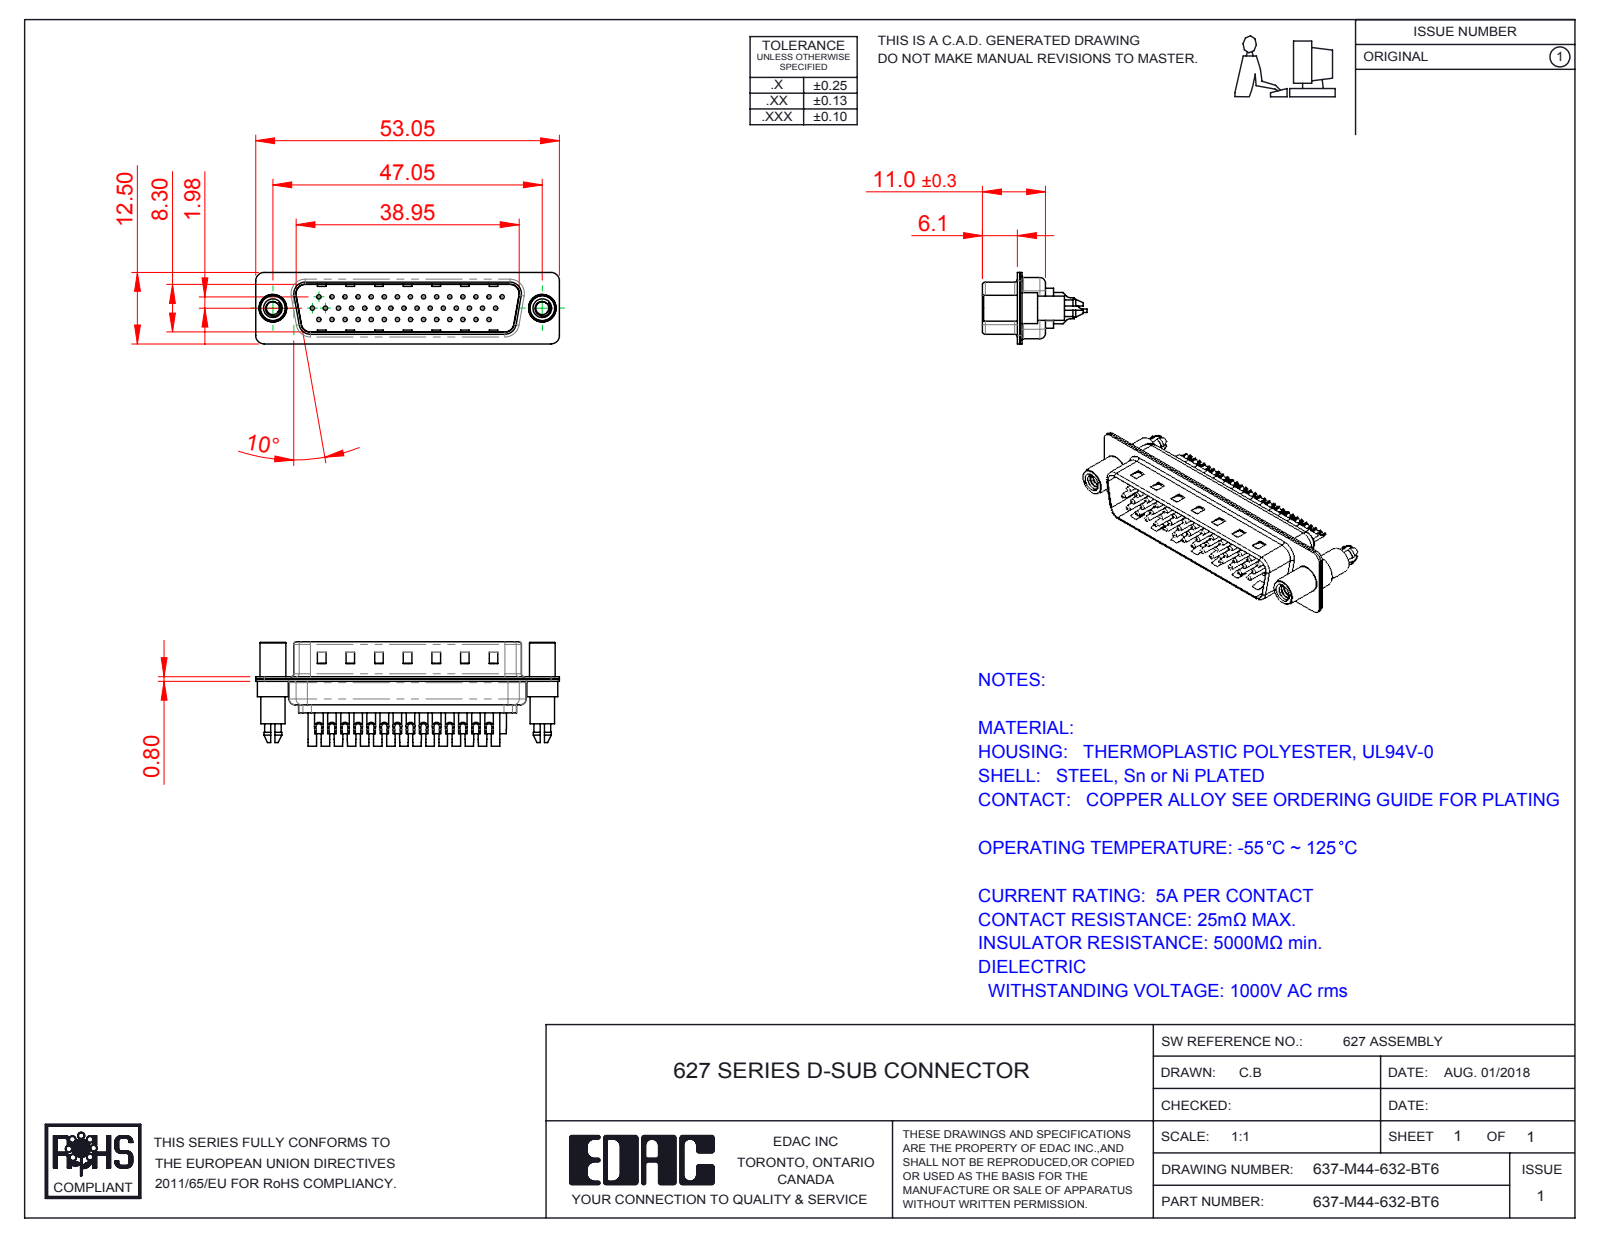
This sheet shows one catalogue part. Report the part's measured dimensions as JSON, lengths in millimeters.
{"part_name": "637M Contact Row 2_32; 637M Shell Front_44 Contacts; 637M Housing_44 Contacts; 637M Contact Row 3_32 (+4 more)", "step_written_by": "SolidWorks 2016 (CONFIG_CONTROL_DESIGN)", "units": "millimeters", "bodies": {"solids": 49, "faces": 2088, "planar": 605, "cylindrical": 877, "other": 606}, "overall_size": [53.05, 18.25, 12.5], "volume_mm3": 3311, "surface_area_mm2": 9494, "round_holes": [[0.75, 44], [1, 44], [1.6, 44], [2, 44], [2.26, 2], [4, 2], [4.8, 2]], "round_bosses_or_shafts": [[1.5, 44], [2, 3], [0.75, 3], [5.4, 2], [4.9, 2], [4.5, 2], [4.25, 2]], "partial_cylinders_radius": [[1.5, 18], [2, 12], [1.6, 10], [0.5, 8], [1, 7], [0.25, 4], [0.6, 4], [0.65, 4]], "face_to_face_distances": [0.4, 0.8, 9.5, 9.1, 8.7, 9.9, 0.75, 1.1, 0.35, 1.9], "hole_center_spacings": [2.28, 3.96, 2.29, 4.57, 8.24, 6.86, 11.43, 14.99]}
